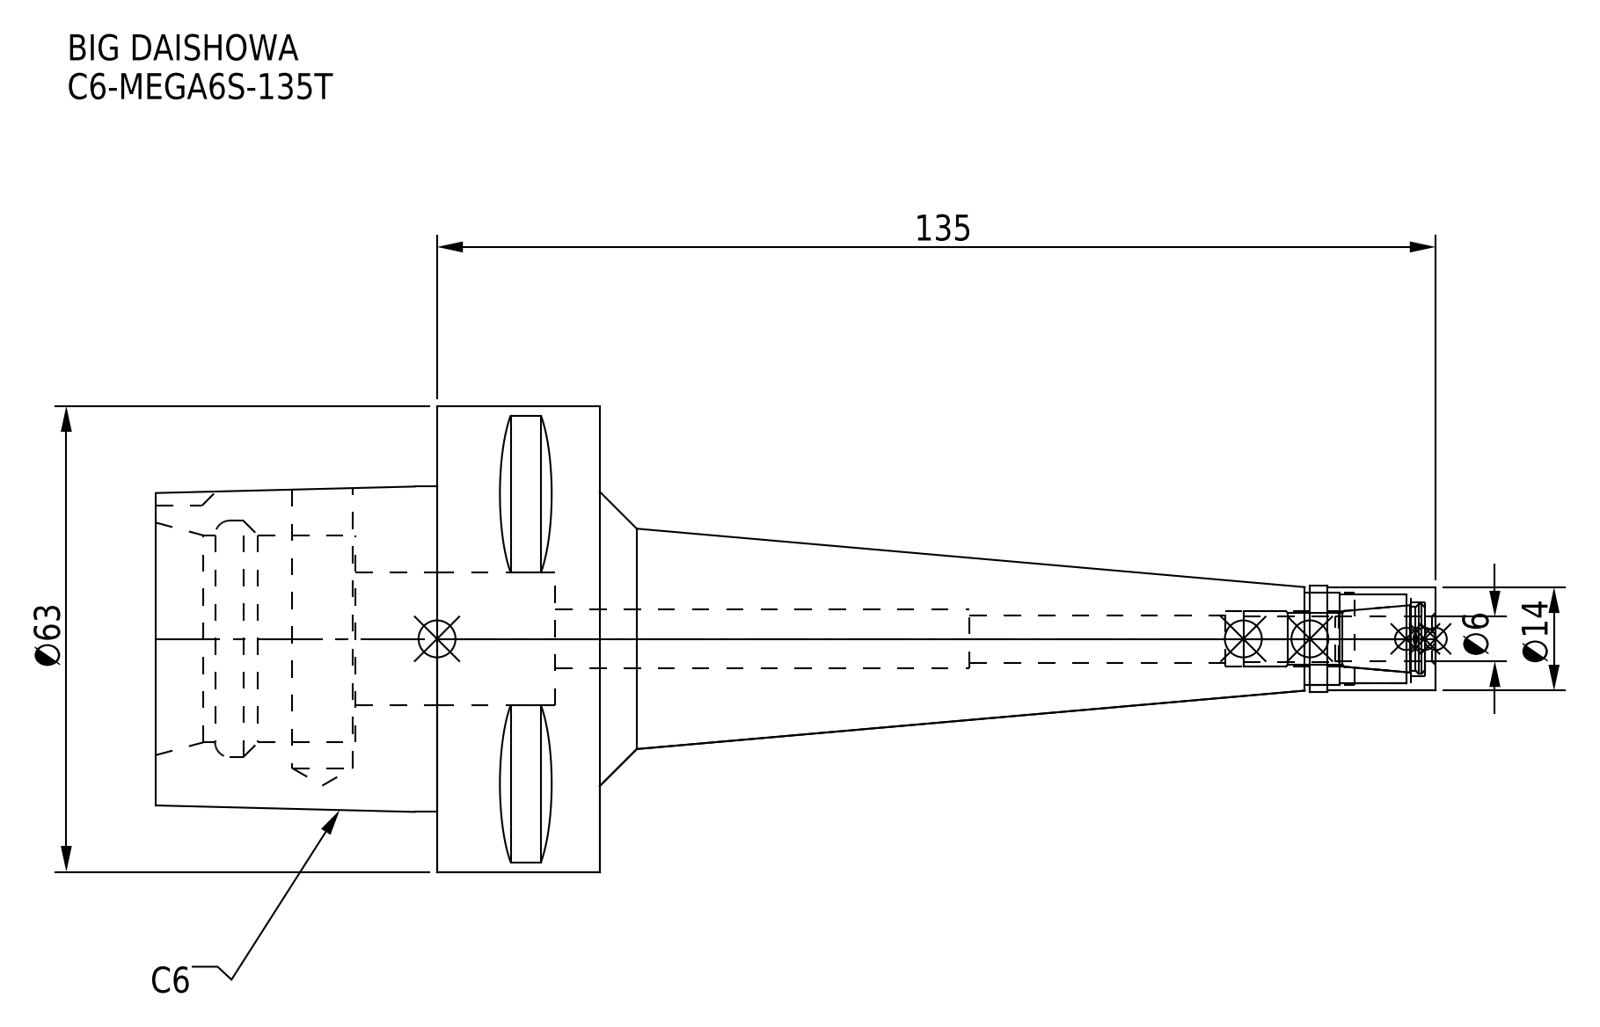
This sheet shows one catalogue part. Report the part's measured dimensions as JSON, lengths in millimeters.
{"part_name": "MGN6S_1.stp; C6-MEGA6S-135T-060-FreeParts; C6-MEGA6S-135T-060.stp; C6-MEGA6S-135T (+3 more)", "step_written_by": "SolidWorks 2019 (CONFIG_CONTROL_DESIGN)", "units": "millimeters", "bodies": {"solids": 2, "faces": 93, "planar": 38, "cylindrical": 37, "other": 18}, "overall_size": [173, 63, 63], "volume_mm3": 134228, "surface_area_mm2": 30813, "round_holes": [[6.1, 1], [6.4, 1], [7.4, 1], [8, 1], [8.1, 1], [10, 1], [12, 1], [12.5, 1], [18, 1], [28, 1], [32, 1]], "round_bosses_or_shafts": [[63, 1], [14.3, 1], [14, 1]], "partial_cylinders_radius": [[5, 1]], "face_to_face_distances": [22, 27, 60, 38, 11, 33, 24.89, 55.4, 6, 16]}
